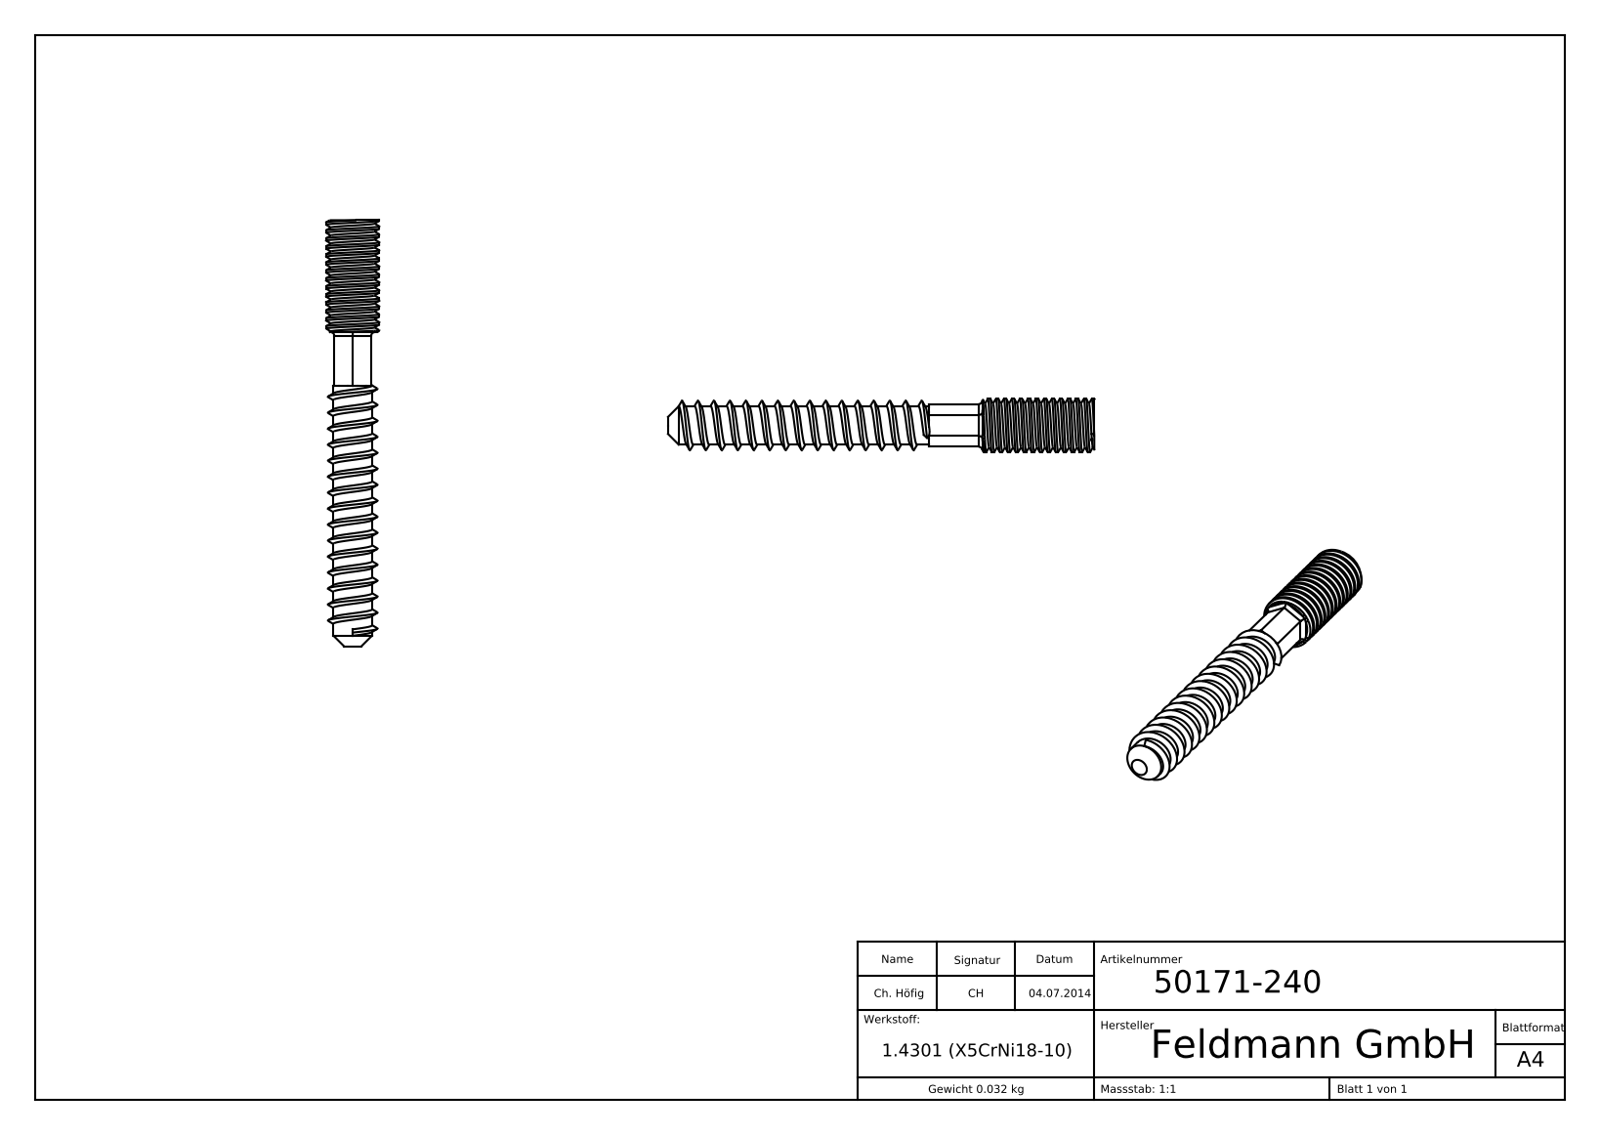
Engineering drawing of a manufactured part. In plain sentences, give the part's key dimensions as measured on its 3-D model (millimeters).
The part is named "50171-240". Its 3-D file was written by "SolidWorks 2015 (CONFIG_CONTROL_DESIGN)". It is 1 solid with 237 faces: 96 planar, 64 cylindrical and 77 other. Overall it measures 80 by 10 by 10 millimeters. Its volume is 4 092 cubic millimeters and its surface area 3 049 square millimeters. Round bosses or shafts: 1 of diameter 10, 1 of diameter 7.2. The main face-to-face distances are 6.92, 80, 21, 59, 31, 10, 49, 3.46, 0.5, 20.5.
